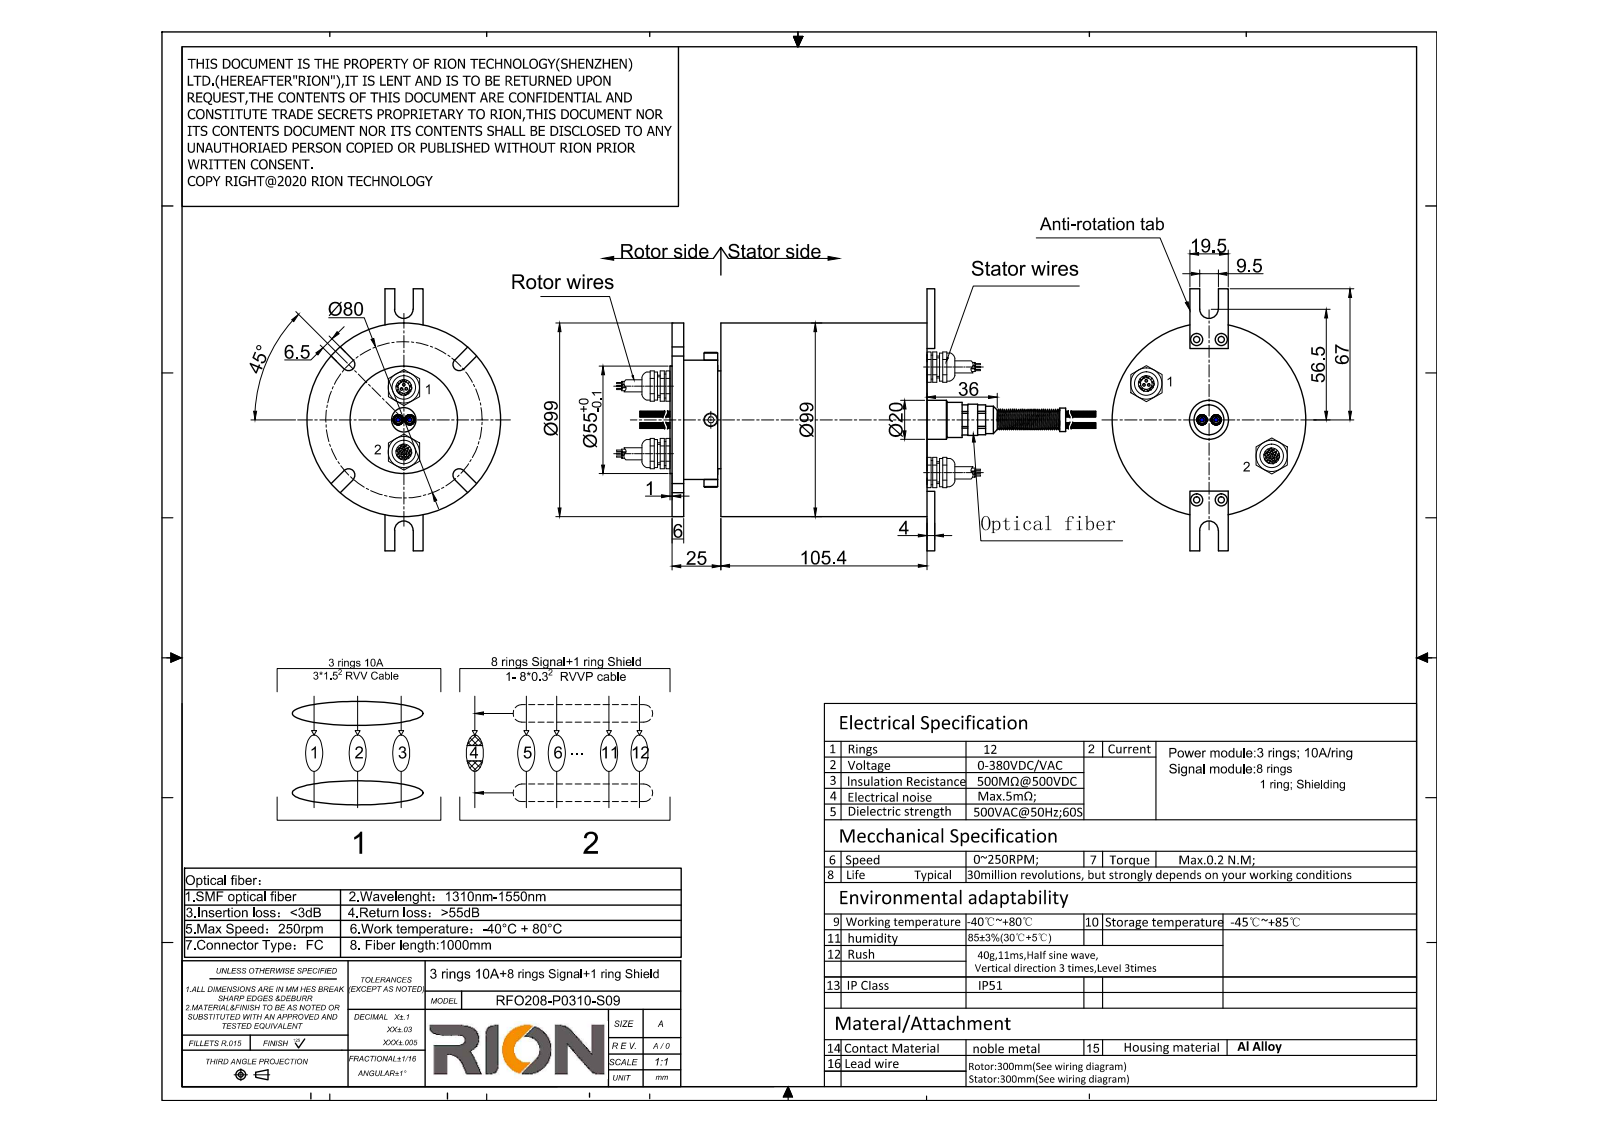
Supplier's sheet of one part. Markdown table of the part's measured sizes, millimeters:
| quantity | value |
| --- | --- |
| part name | RFO208-P0310-S09 |
| STEP written by | SolidWorks 2014 (CONFIG_CONTROL_DESIGN) |
| units | millimeters |
| bodies | 1 solid, 298 faces (142 planar, 126 cylindrical, 30 other) |
| overall size | 252.4 × 134 × 99 |
| volume | 953 918 mm³ |
| surface area | 76 735 mm² |
| round holes (diameter × count) | 3.2 × 4 |
| round bosses / shafts (diameter × count) | 12 × 5, 15 × 4, 8 × 4, 3 × 2, 2 × 2, 99 × 1, 68 × 1, 55 × 1 |
| partial cylindrical surfaces (radius × count) | 3.25 × 4, 4.75 × 2 |
| main face-to-face distances | 105.4, 25, 130.4, 6, 19, 124.4, 1, 7, 26, 131.4 |
| hole center spacings | 12.7, 82, 82.98 |
